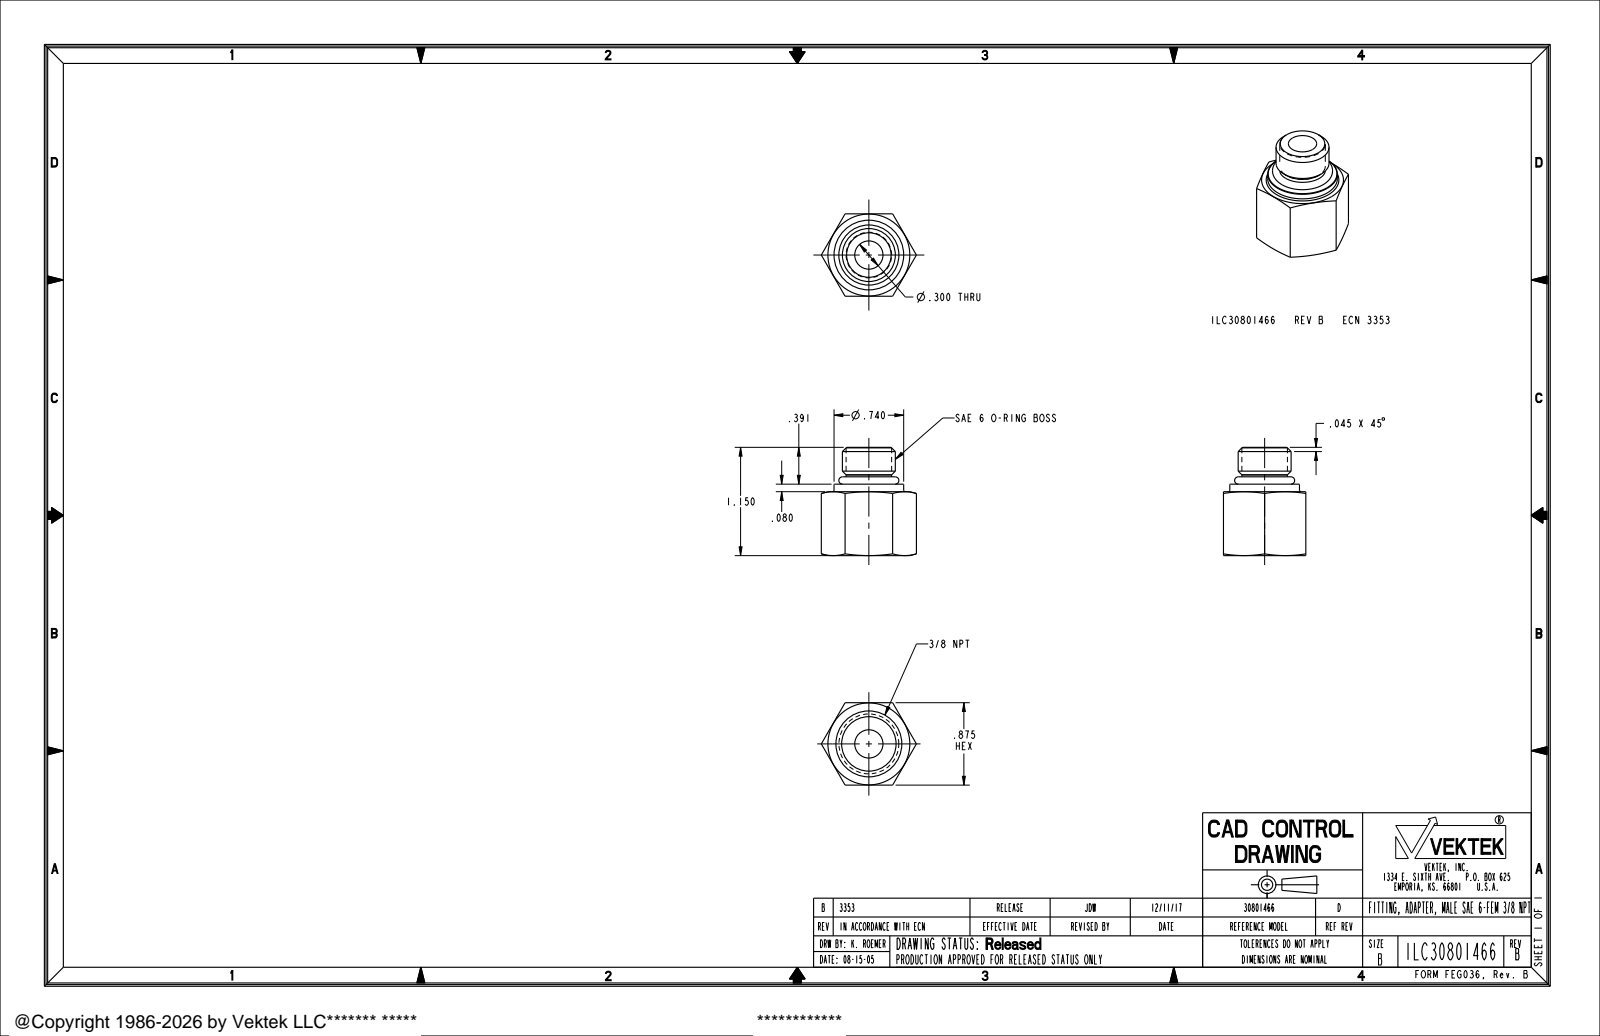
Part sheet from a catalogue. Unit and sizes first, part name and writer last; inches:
Units: inches
Overall size (bounding box): 1.15 × 1.01 × 0.875
Round holes (diameter × count): ⌀0.3 ×1, ⌀0.578 ×1
Round bosses / shafts (diameter × count): ⌀0.74 ×1, ⌀0.636 ×1, ⌀0.563 ×1, ⌀0.482 ×1
Main face-to-face distances: 0.875, 0.759, 0.08, 0.679, 0.391, 0.471, 1.15, 0.63, 0.239, 0.159
Volume: 0.369 in³ · Surface area: 7.056 in²
Bodies: 2 solids, 43 faces (11 planar, 12 cylindrical, 20 other)
Part name (STEP PRODUCT): ILC30801466
STEP written by: PRO/ENGINEER BY PARAMETRIC TECHNOLOGY CORPORATION, 2013320 (AUTOMOTIVE_DESIGN)
